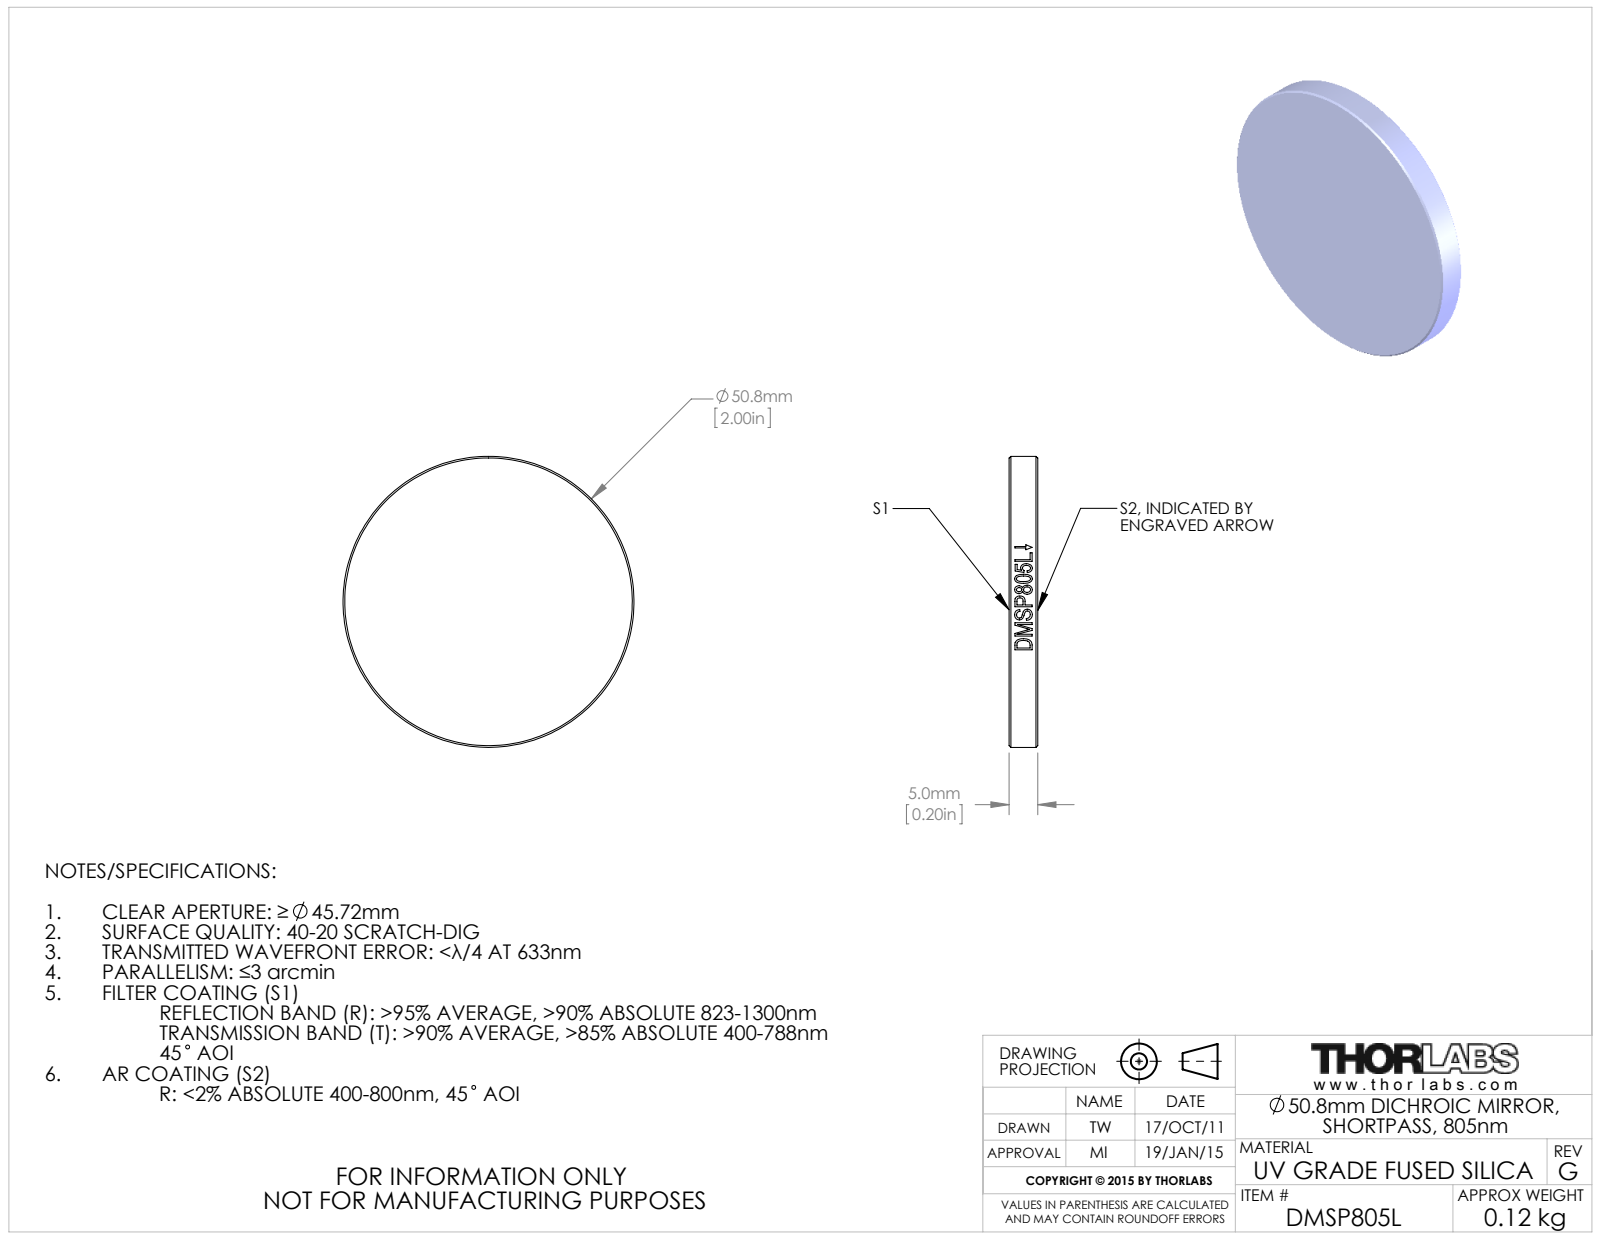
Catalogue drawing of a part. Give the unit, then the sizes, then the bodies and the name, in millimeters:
Units: millimetres
Overall size (bounding box): 50.8 × 50.8 × 5
Round bosses / shafts (diameter × count): ⌀50.8 ×1
Main face-to-face distances: 5
Bodies: 0 solids, 22 faces (2 planar, 16 cylindrical, 4 other)
Part name (STEP PRODUCT): 21945-E0W
STEP written by: SolidWorks 2011 (CONFIG_CONTROL_DESIGN)
